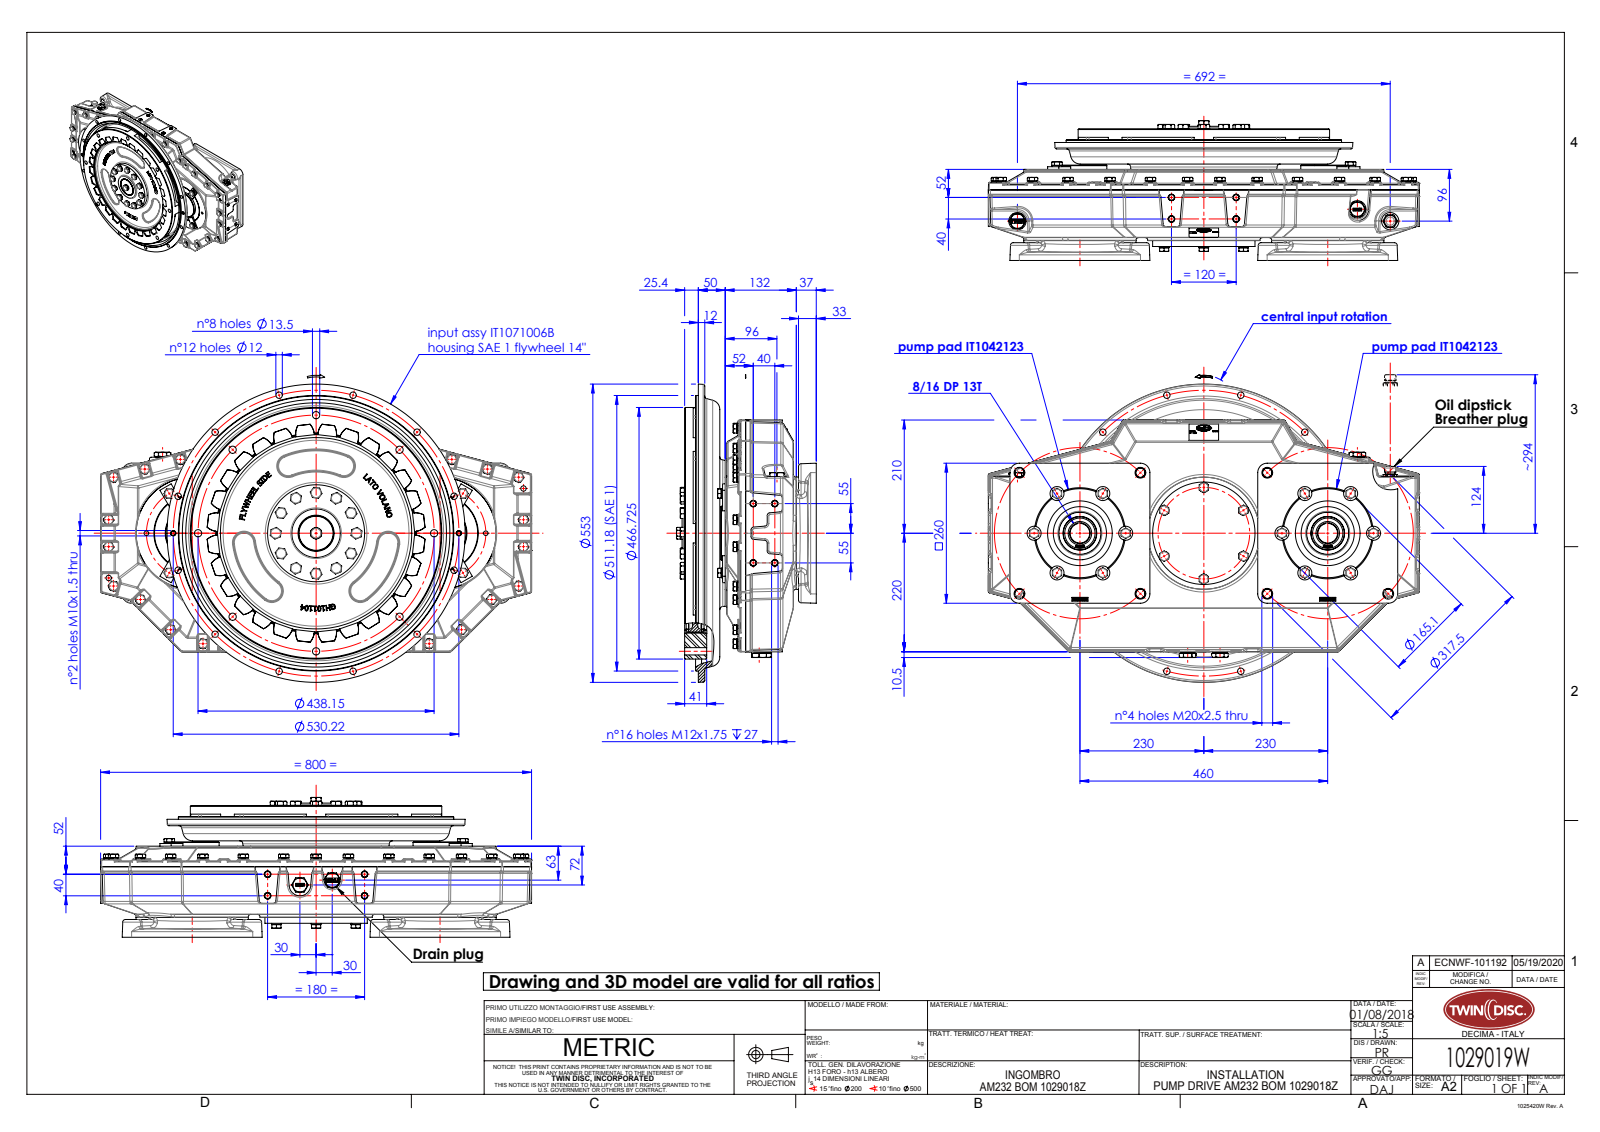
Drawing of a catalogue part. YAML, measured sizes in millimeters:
part_name: "IT2021216_rev03-installation; ITam230-001_rev01-installation; ITam232-002_rev00-installation; IT4588040_rev00-installation (+6 more)"
step_written_by: "SolidWorks 2019 (AUTOMOTIVE_DESIGN)"
units: millimeters
bodies: {solids: 32, faces: 8840, planar: 3829, cylindrical: 2289, other: 2722}
overall_size: [800, 571.17, 259.5]
volume: 11430000
surface_area: 4086000
round_holes:
  - {diameter: 10.2, count: 58}
  - {diameter: 8.5, count: 32}
  - {diameter: 10.5, count: 29}
  - {diameter: 12, count: 24}
  - {diameter: 13, count: 20}
  - {diameter: 11, count: 18}
  - {diameter: 26, count: 12}
  - {diameter: 10, count: 10}
  - {diameter: 13.5, count: 8}
  - {diameter: 17.5, count: 8}
  - {diameter: 12.2, count: 7}
  - {diameter: 18.5, count: 3}
round_bosses_or_shafts:
  - {diameter: 10, count: 49}
  - {diameter: 16.2, count: 47}
  - {diameter: 18.1, count: 39}
  - {diameter: 18, count: 19}
  - {diameter: 12, count: 19}
  - {diameter: 24, count: 12}
  - {diameter: 20, count: 9}
  - {diameter: 21.1, count: 7}
partial_cylinders:
  - {radius: 2, count: 284}
  - {radius: 5, count: 142}
  - {radius: 0.75, count: 112}
  - {radius: 3, count: 80}
  - {radius: 2.5, count: 76}
  - {radius: 0.45, count: 58}
  - {radius: 34, count: 56}
  - {radius: 34.2, count: 56}
face_to_face_distances: [10, 38, 58, 48, 20, 152, 50.9, 94, 142, 132]
hole_center_spacings: [120, 57.4, 75, 138.58, 40, 150, 207.84, 30]
